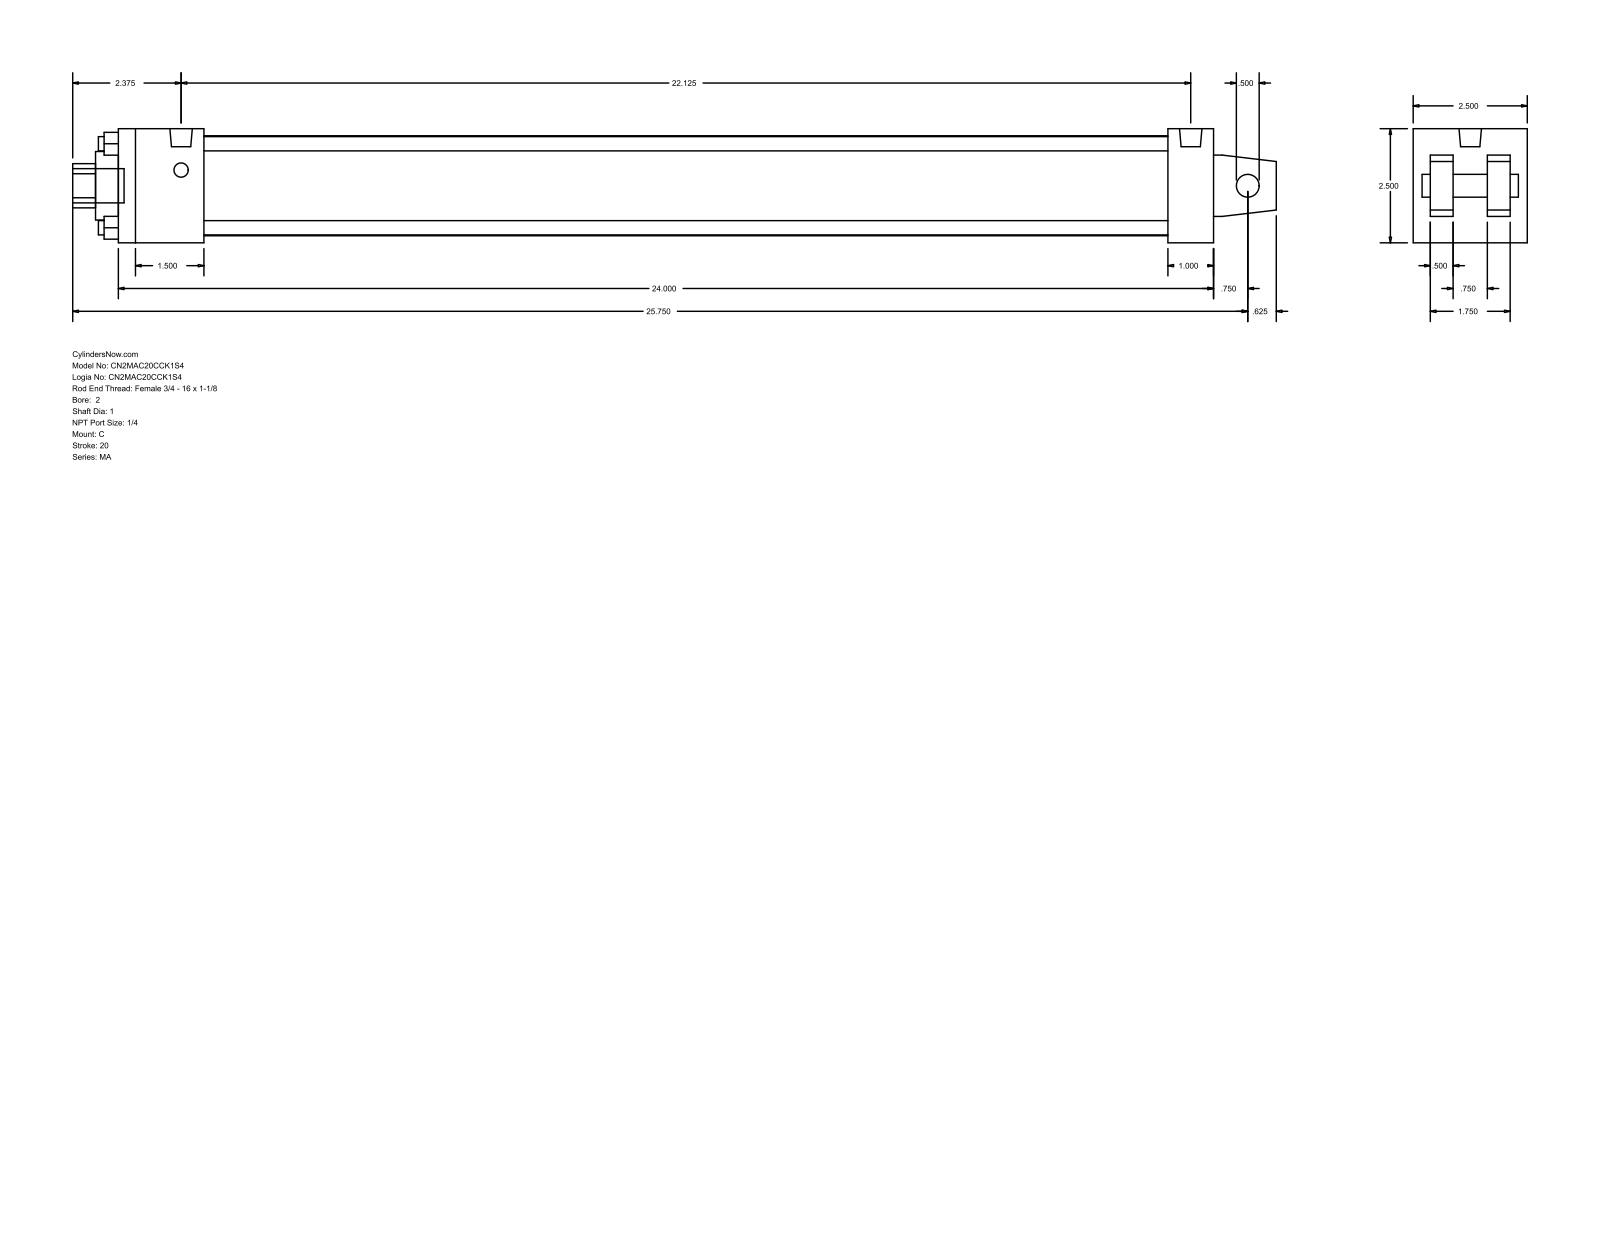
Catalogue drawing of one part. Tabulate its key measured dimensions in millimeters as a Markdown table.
| quantity | value |
| --- | --- |
| part name | MA_C__0200_1 |
| STEP written by | GSSL Pune (CONFIG_CONTROL_DESIGN) |
| units | millimeters |
| bodies | 0 solids, 103 faces (76 planar, 27 cylindrical, 0 other) |
| overall size | 669.92 × 63.5 × 63.5 |
| round holes (diameter × count) | 7.94 × 4, 12.7 × 1, 25.4 × 1, 38.1 × 1, 55.63 × 1 |
| round bosses / shafts (diameter × count) | 7.94 × 4, 12.49 × 2, 19.05 × 1 |
| partial cylindrical surfaces (radius × count) | 12.29 × 1 |
| main face-to-face distances | 63.5, 12.7, 609.6, 22.22, 41.28, 9.52, 53.98, 31.76, 47.63, 25.4 |
| hole center spacings | 33.05, 46.74, 66.1 |
